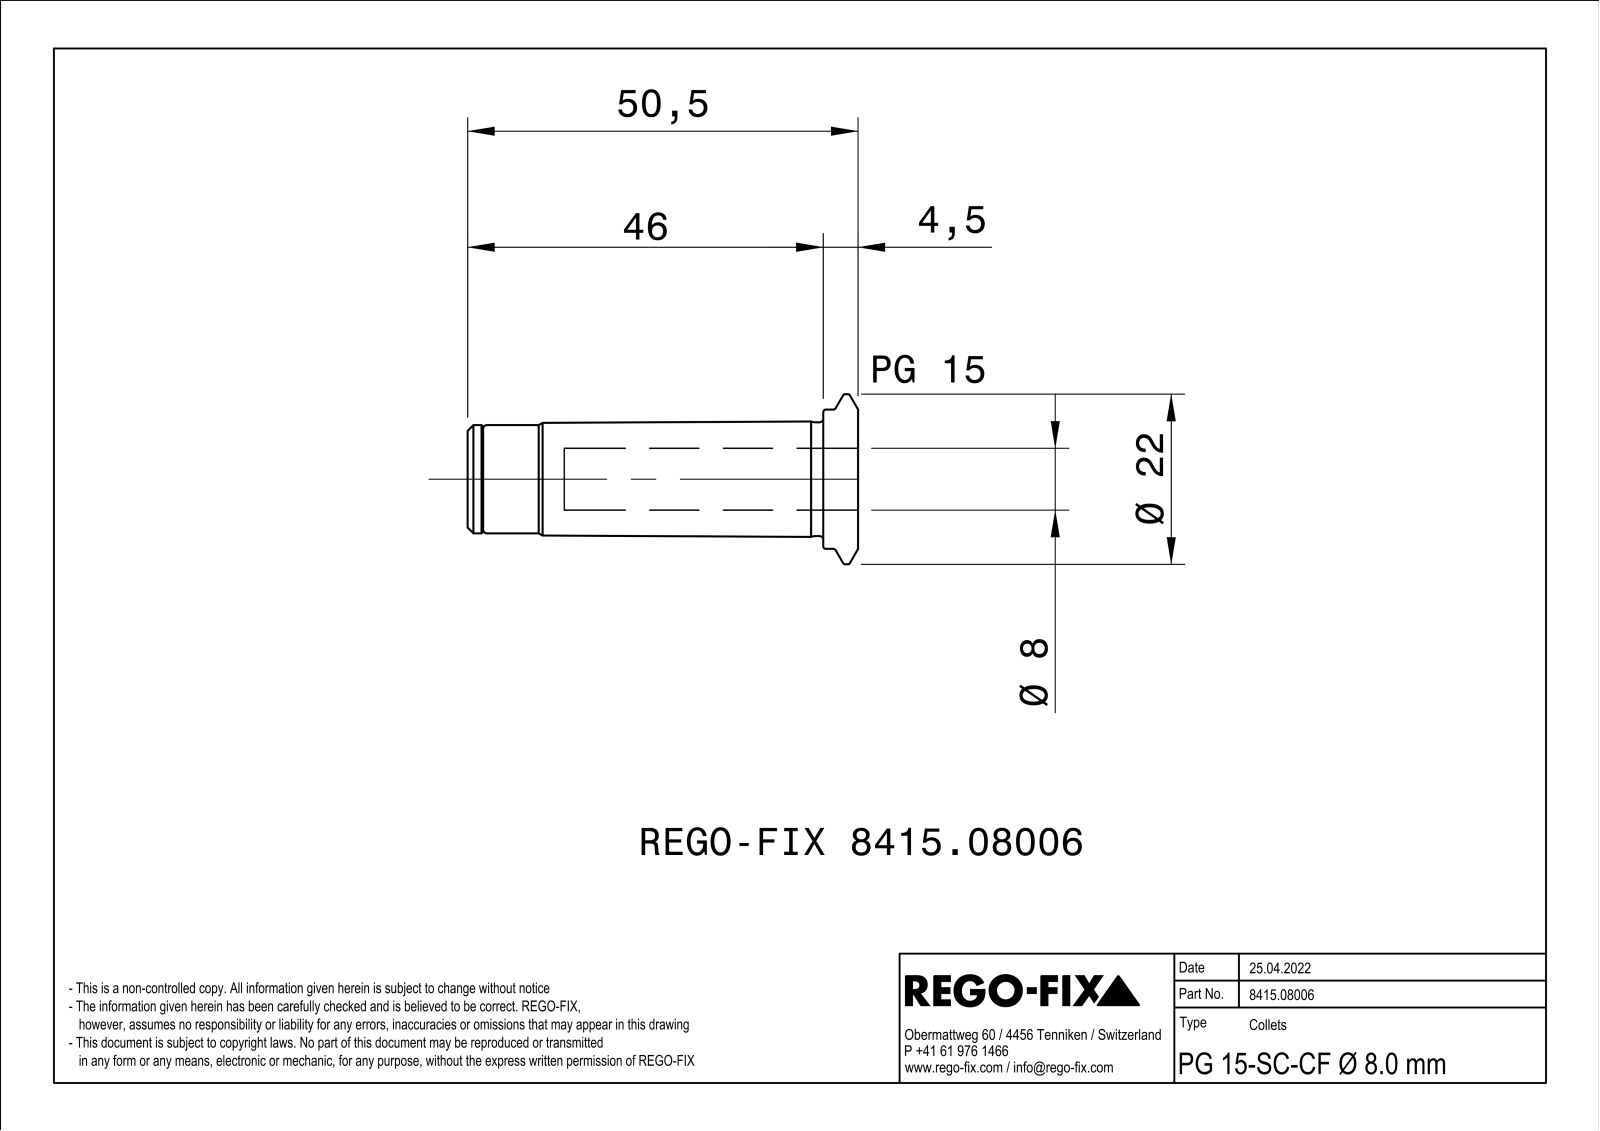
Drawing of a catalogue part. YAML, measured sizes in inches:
part_name: "0024149"
step_written_by: "SIEMENS PLM Software Solid Edge ST10 (AUTOMOTIVE_DESIGN)"
units: inches
bodies: {solids: 2, faces: 125, planar: 47, cylindrical: 37, other: 41}
overall_size: [1.988, 0.866, 0.866]
volume: 0.379
surface_area: 9.024
round_holes:
  - {diameter: 0.059, count: 2}
  - {diameter: 0.272, count: 1}
  - {diameter: 0.283, count: 1}
  - {diameter: 0.323, count: 1}
  - {diameter: 0.43, count: 1}
  - {diameter: 0.48, count: 1}
round_bosses_or_shafts:
  - {diameter: 0.866, count: 1}
  - {diameter: 0.709, count: 1}
  - {diameter: 0.579, count: 1}
  - {diameter: 0.551, count: 1}
partial_cylinders:
  - {radius: 0.006, count: 4}
  - {radius: 0.031, count: 4}
  - {radius: 0.157, count: 1}
  - {radius: 0.205, count: 1}
  - {radius: 0.236, count: 1}
face_to_face_distances: [1.909, 0.216, 0.079, 1.988, 0.315, 0.118, 0.183, 0.171, 0.177, 1.732]
